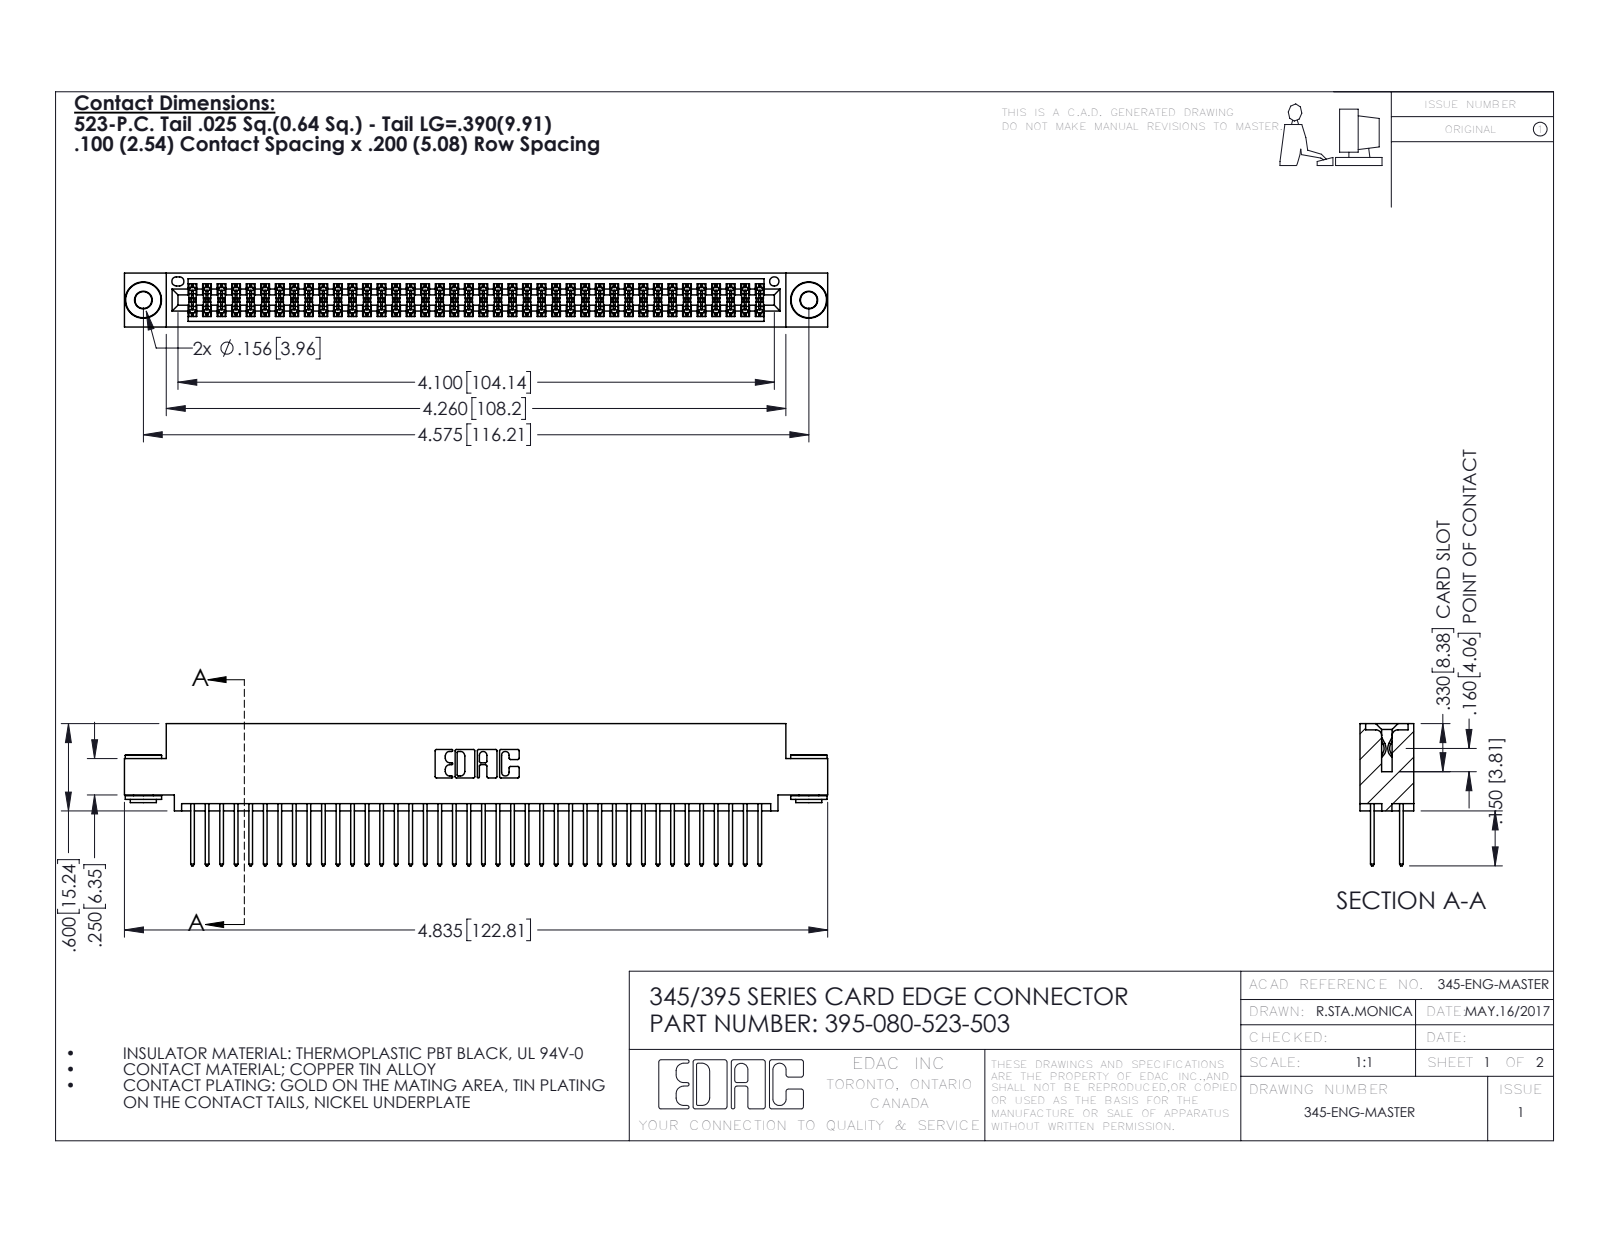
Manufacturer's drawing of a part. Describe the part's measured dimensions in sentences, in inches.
The part is named "345 Part_0.110 Offset - 0.156 Dia-TH; 395-080-523-503; 345-250-002_345-250-002-102; 345-292-001_345-293-123". Its 3-D file was written by "SolidWorks 2016 (CONFIG_CONTROL_DESIGN)". It is 83 solids with 4168 faces: 2734 planar, 1426 cylindrical and 8 other. Overall it measures 4.835 by 0.977 by 0.37 inches. Its volume is 0.734 cubic inches and its surface area 29.08 square inches. Round holes: 2 of diameter 0.116, 2 of diameter 0.156, 1 of diameter 0.064. Round bosses or shafts: 2 of diameter 0.25, 2 of diameter 0.18, 2 of diameter 0.136. Partial cylindrical surfaces (rounded edges, fillets, slot ends): 120 of radius 0.006, 80 of radius 0.01, 22 of radius 0.01, 6 of radius 0.007, 6 of radius 0.031, 3 of radius 0.026, 2 of radius 0.014, 2 of radius 0.019. The main face-to-face distances are 0.072, 0.298, 0.2, 0.025, 0.098, 0.272, 0.37, 0.225, 0.175, 0.149. The hole center spacings are 0.27, 4.339, 4.575.
